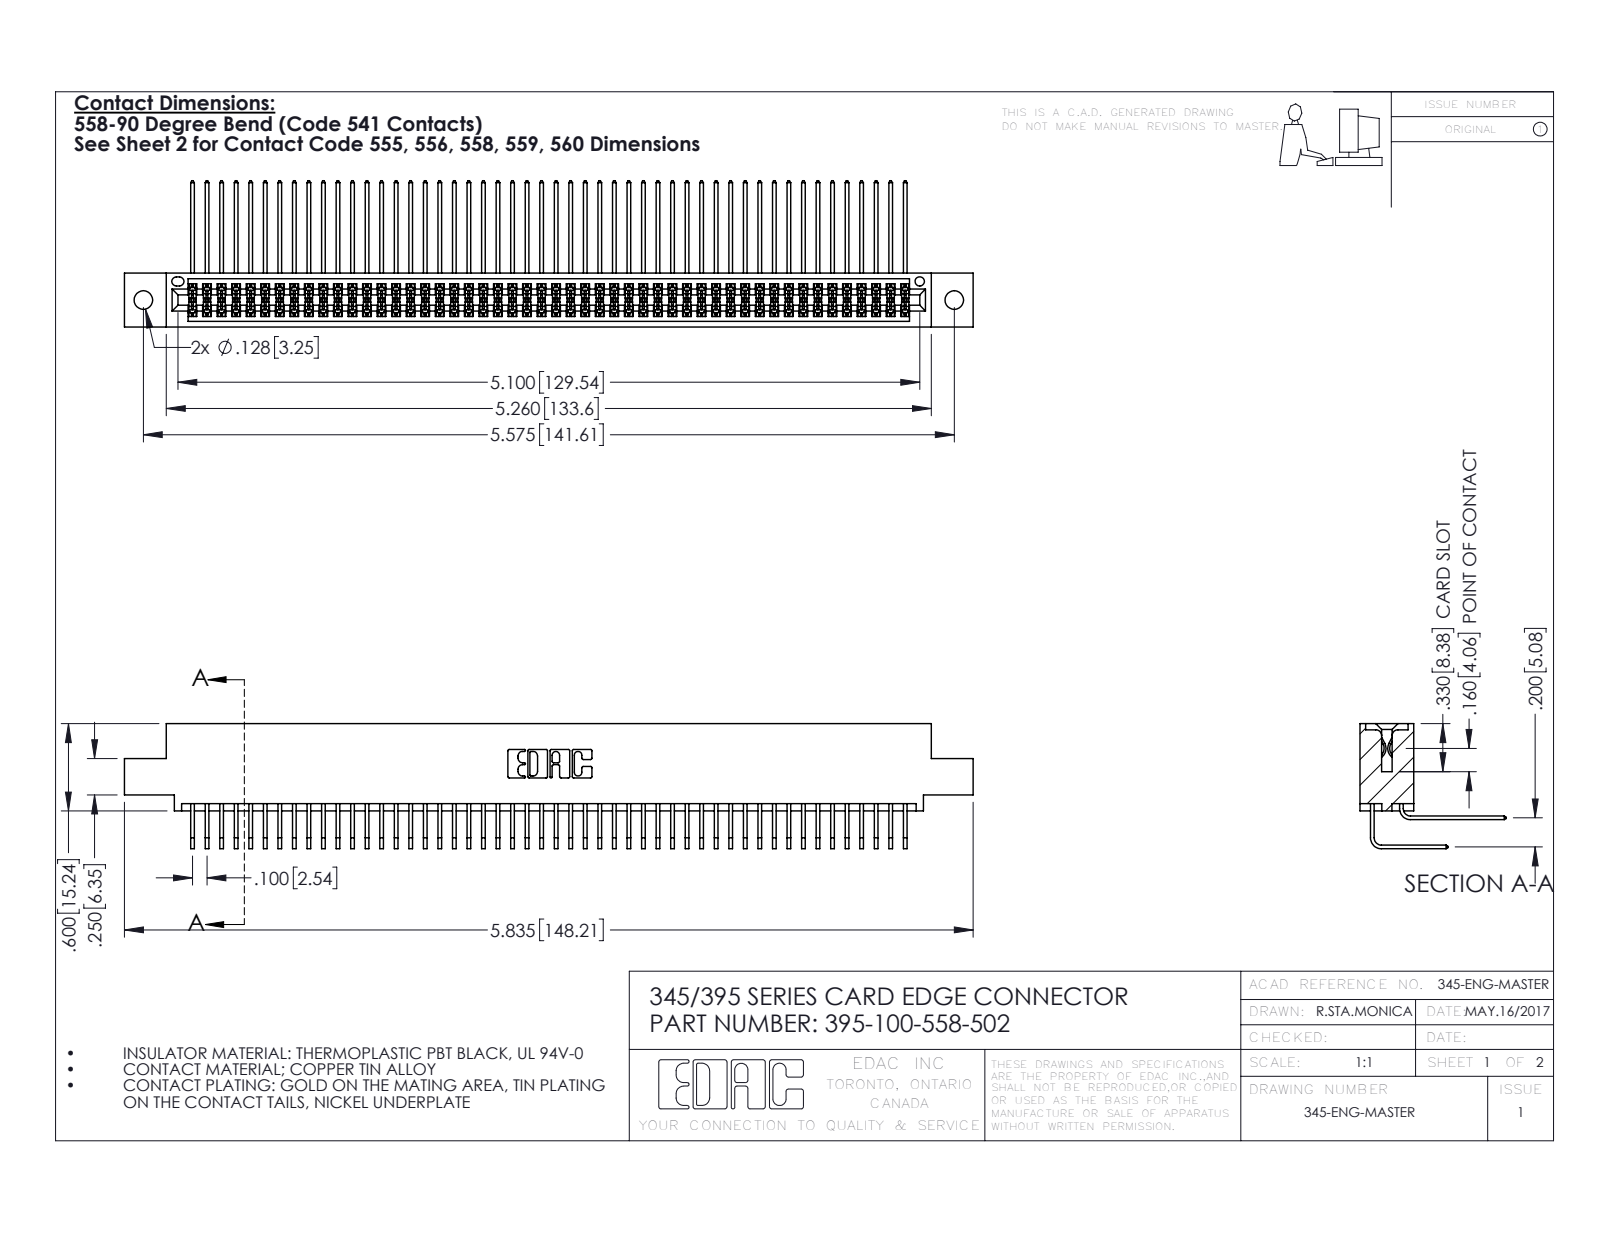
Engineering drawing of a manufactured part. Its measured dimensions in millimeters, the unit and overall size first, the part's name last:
Units: millimetres
Overall size (bounding box): 148.2 × 25.5 × 21.8
Round holes (diameter × count): ⌀3.3 ×2, ⌀1.6 ×1
Partial cylindrical surfaces — rounded edges, fillets, slot ends (radius × count): R0.2 ×151, R0.3 ×22, R0.2 ×6, R0.8 ×6, R0.7 ×3, R0.4 ×2, R0.5 ×2, R0.6 ×2
Main face-to-face distances: 1.8, 7.6, 5.1, 9.4, 2.5, 6.9, 0.6, 5.7, 0.6, 4.4
Hole centre spacings: 6.9, 135.6, 141.6
Volume: 14 900 mm³ · Surface area: 24 770 mm²
Bodies: 101 solids, 5330 faces (3584 planar, 1746 cylindrical, 0 other)
Part name (STEP PRODUCT): 345-292-001_558 Tail - 2; 345 Part_0.110 Offset - 0.128 Dia; 395-100-558-502; 345-292-001_558 559 Tail - 1
STEP written by: SolidWorks 2016 (CONFIG_CONTROL_DESIGN)
